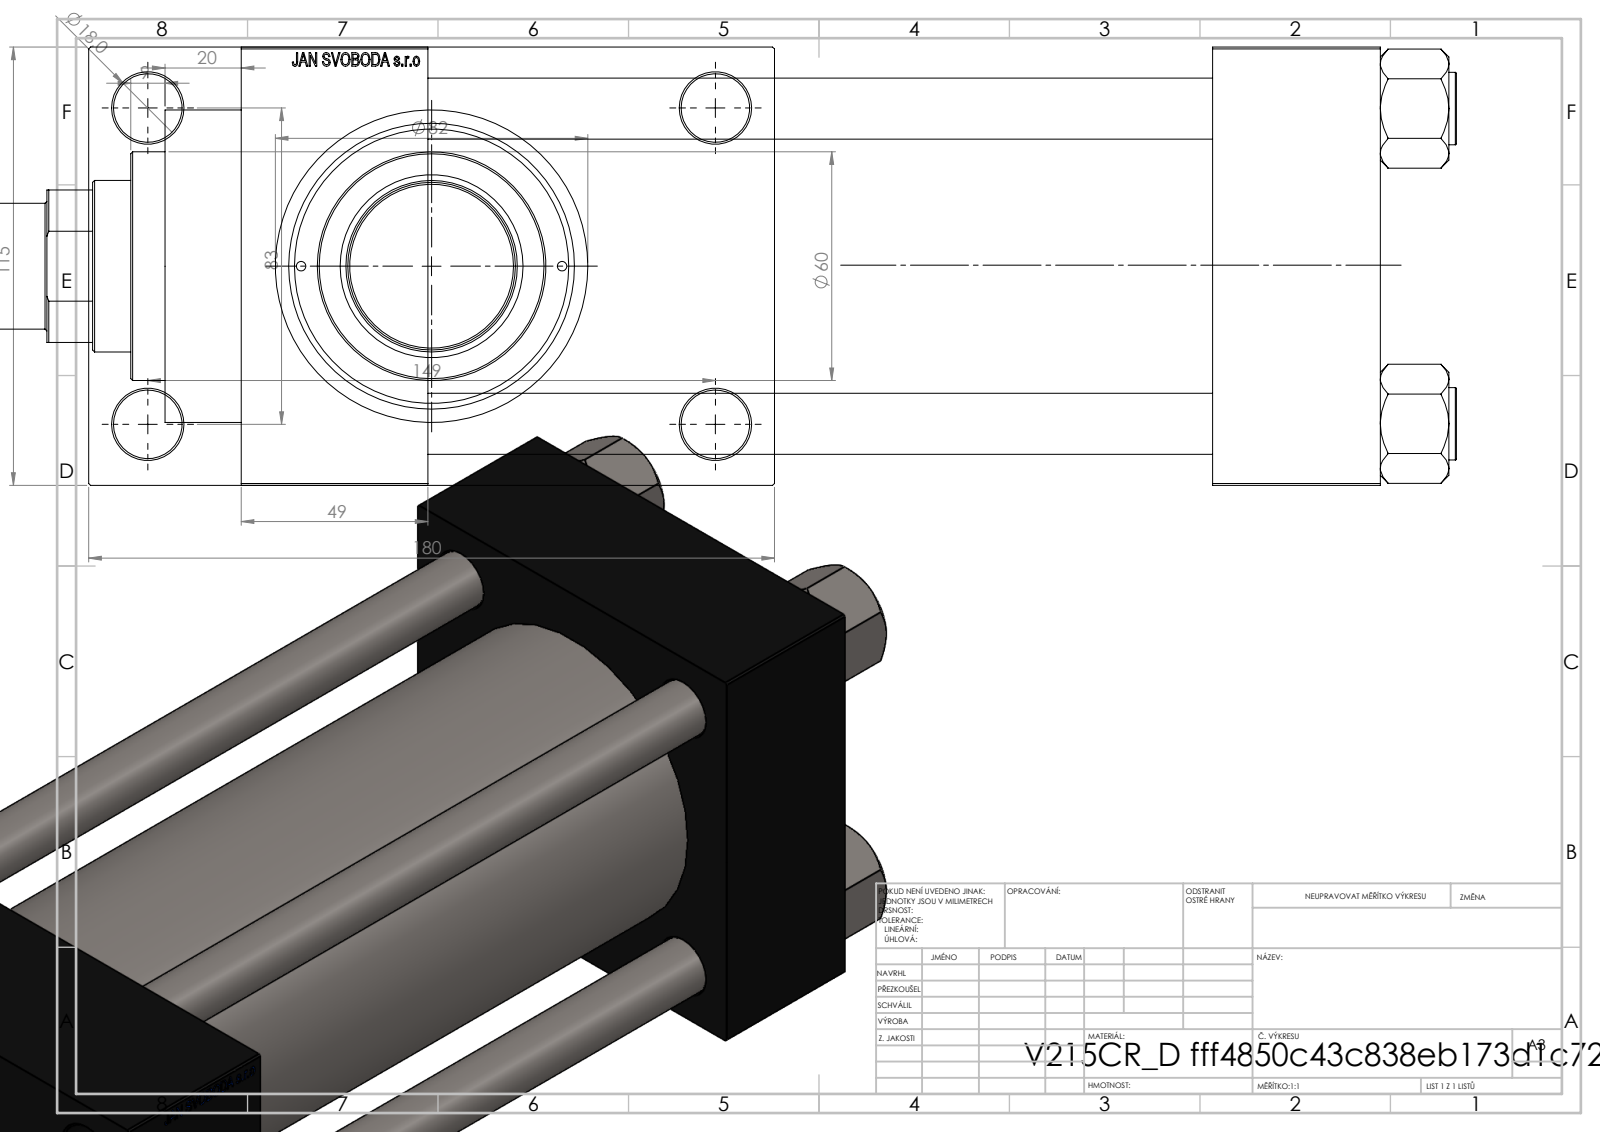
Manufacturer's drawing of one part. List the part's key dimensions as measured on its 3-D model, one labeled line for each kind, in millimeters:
Part name (STEP PRODUCT): V215CR_VCP_D; V215CR_ROD_END_F; NUT_M5_D; V215CR_D_TYCINKA (+2 more)
STEP written by: SolidWorks 2019 (CONFIG_CONTROL_DESIGN)
Units: millimetres
Bodies: 12 solids, 1172 faces (550 planar, 96 cylindrical, 526 other)
Overall size (bounding box): 414 × 180 × 115
Volume: 2 501 000 mm³ · Surface area: 431 661 mm²
Round holes (diameter × count): ⌀16 ×4, ⌀18 ×4, ⌀2.5 ×2, ⌀7 ×2, ⌀26.44 ×2, ⌀35 ×2, ⌀31.5 ×1, ⌀45 ×1, ⌀48 ×1, ⌀61 ×1, ⌀72 ×1, ⌀80 ×1
Round bosses / shafts (diameter × count): ⌀19 ×4, ⌀86 ×1, ⌀82 ×1, ⌀60 ×1, ⌀44 ×1, ⌀33 ×1
Main face-to-face distances: 115, 44, 206, 255, 49, 250, 299, 32.5, 147.5, 180
Hole centre spacings: 33.15, 41.96, 57.81, 58.48, 82.7, 85.28, 86.17, 89.24
